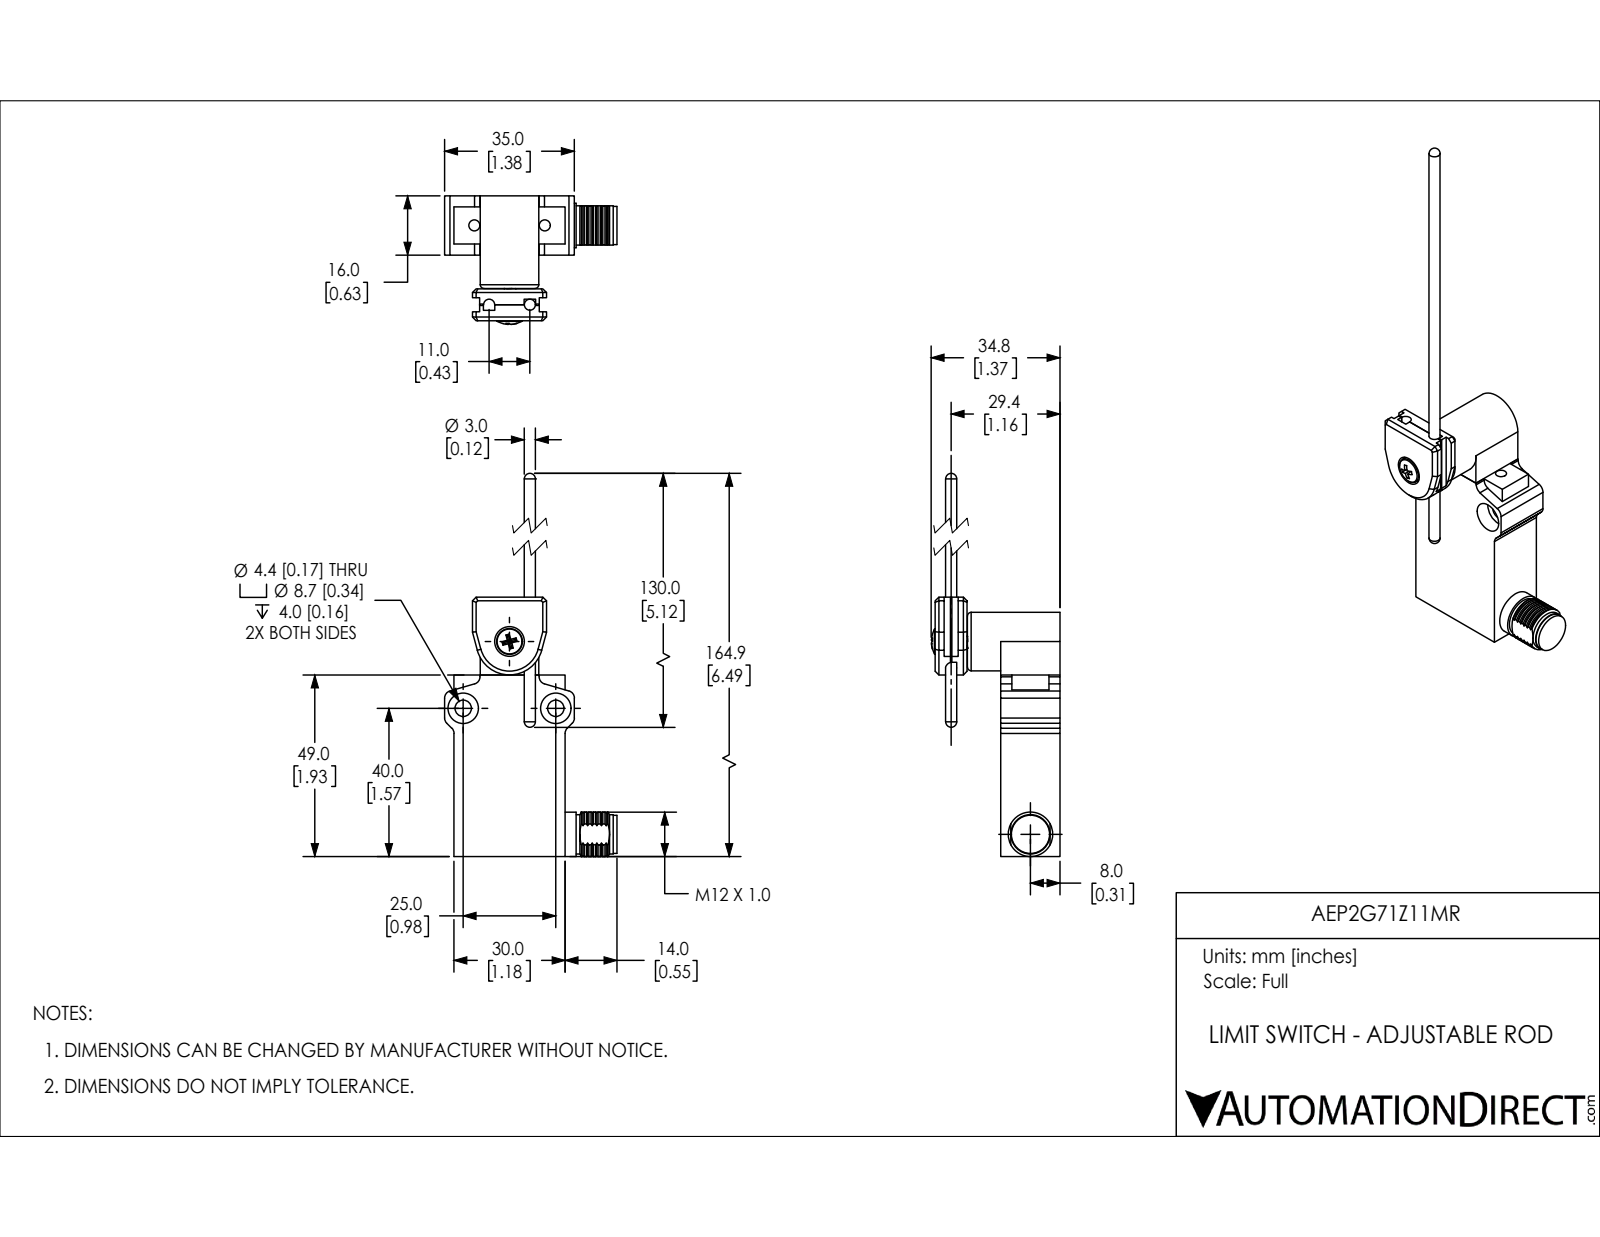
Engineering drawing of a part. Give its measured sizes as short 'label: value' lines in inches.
name: AEP2G71Z11MR
written by: SolidWorks 2018 (AUTOMOTIVE_DESIGN)
unit: in
bodies: 7 solids, 346 faces (143 planar, 141 cylindrical, 62 other)
size: 6.49 × 1.831 × 1.366
volume: 1.978 in³; area: 20.32 in²
holes: 2× ⌀0.118, 2× ⌀0.173, 2× ⌀0.323, 1× ⌀0.197, 1× ⌀0.315
bosses: 1× ⌀0.622, 1× ⌀0.472, 1× ⌀0.417, 1× ⌀0.406, 1× ⌀0.276, 1× ⌀0.138, 1× ⌀0.118
rounds: 8× R0.079, 1× R0.059, 1× R0.173, 1× R0.256, 1× R0.26, 1× R0.354
face distances: 0.63, 1.181, 1.929, 0.169, 0.472, 0.28, 0.902, 0.988, 1, 0.697
hole spacings: 0.863, 0.748, 0.984
